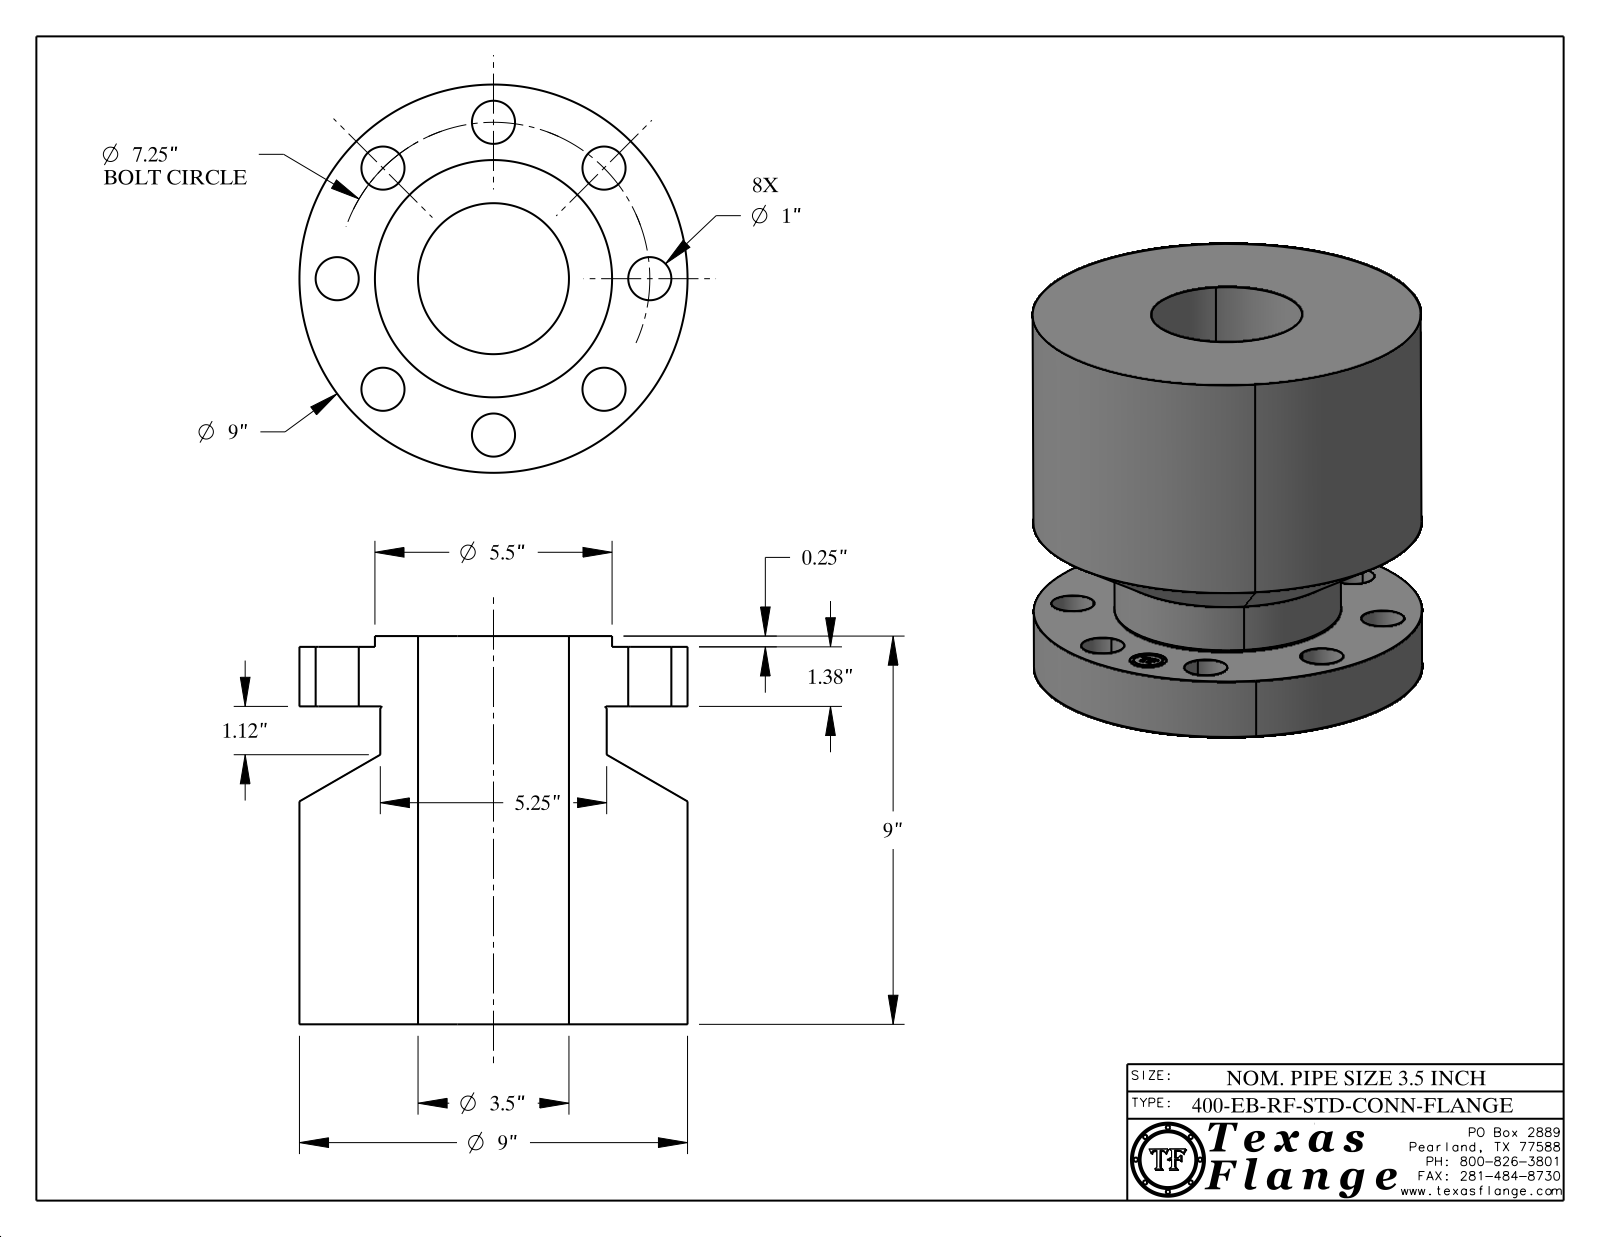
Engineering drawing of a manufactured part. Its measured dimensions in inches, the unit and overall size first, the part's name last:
Units: inches
Overall size (bounding box): 9 × 9 × 9
Round holes (diameter × count): ⌀1 ×8, ⌀0.85 ×1, ⌀3.5 ×1
Round bosses / shafts (diameter × count): ⌀0.051 ×8, ⌀9 ×1, ⌀5.5 ×1, ⌀5.25 ×1, ⌀0.67 ×1
Main face-to-face distances: 7.37, 1.38, 8.75, 0.25, 1.63, 9, 1.625, 1.375, 7.375, 0.254
Hole centre spacings: 3.625, 2.774, 5.127, 6.698, 7.25, 1.415, 7.111, 4.028
Volume: 395.6 in³ · Surface area: 528.1 in²
Bodies: 1 solid, 421 faces (369 planar, 46 cylindrical, 6 other)
Part name (STEP PRODUCT): 3.5-400-EB-RF-STD-CONN-FLANGE
STEP written by: CATIA V5 STEP AP214 (AUTOMOTIVE_DESIGN)
